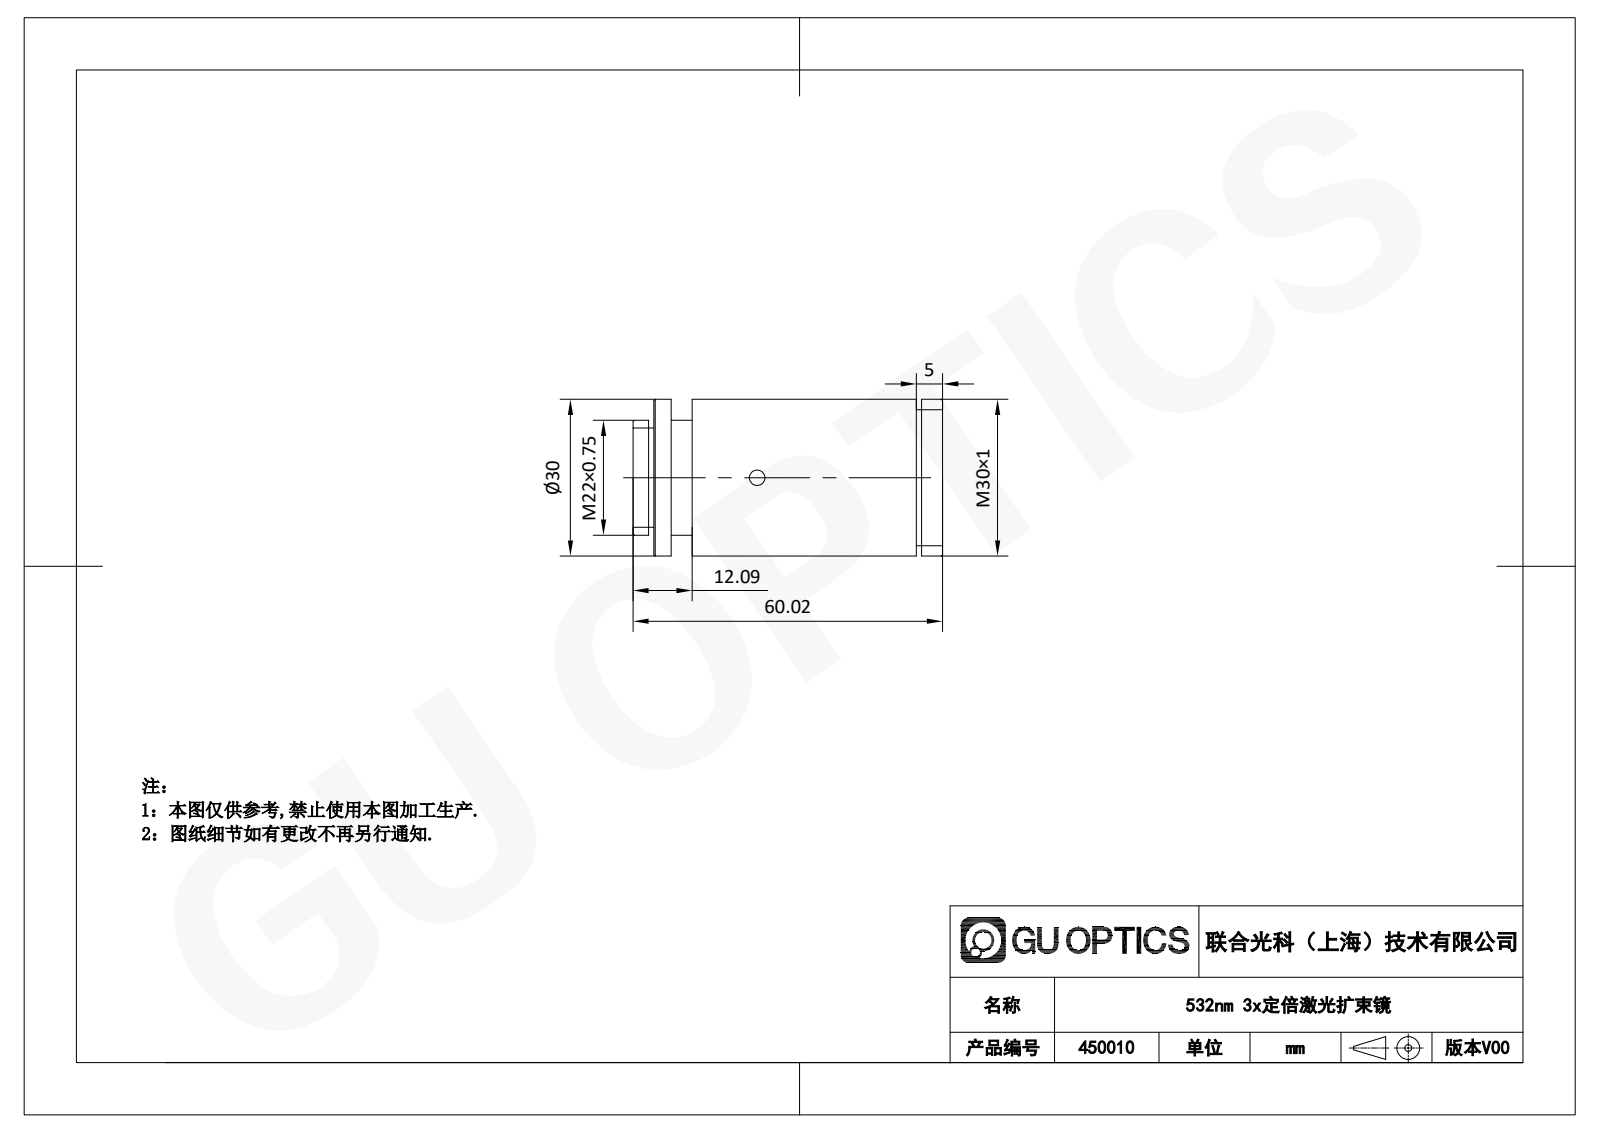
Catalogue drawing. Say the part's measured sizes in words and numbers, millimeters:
The part is named "450010". Its 3-D file was written by "SolidWorks 2020 (AUTOMOTIVE_DESIGN)". It is 1 solid with 43 faces: 11 planar, 22 cylindrical and 10 other. Overall it measures 60.02 by 30 by 30 millimeters. Its volume is 32 292 cubic millimeters and its surface area 10 680 square millimeters. Round holes: 1 of diameter 8, 1 of diameter 18. Round bosses or shafts: 1 of diameter 30, 1 of diameter 26, 1 of diameter 22, 1 of diameter 19. The main face-to-face distances are 4, 56.02, 47.93, 8.09, 52.02, 4.09, 51.93, 43.93, 1, 12.09.
